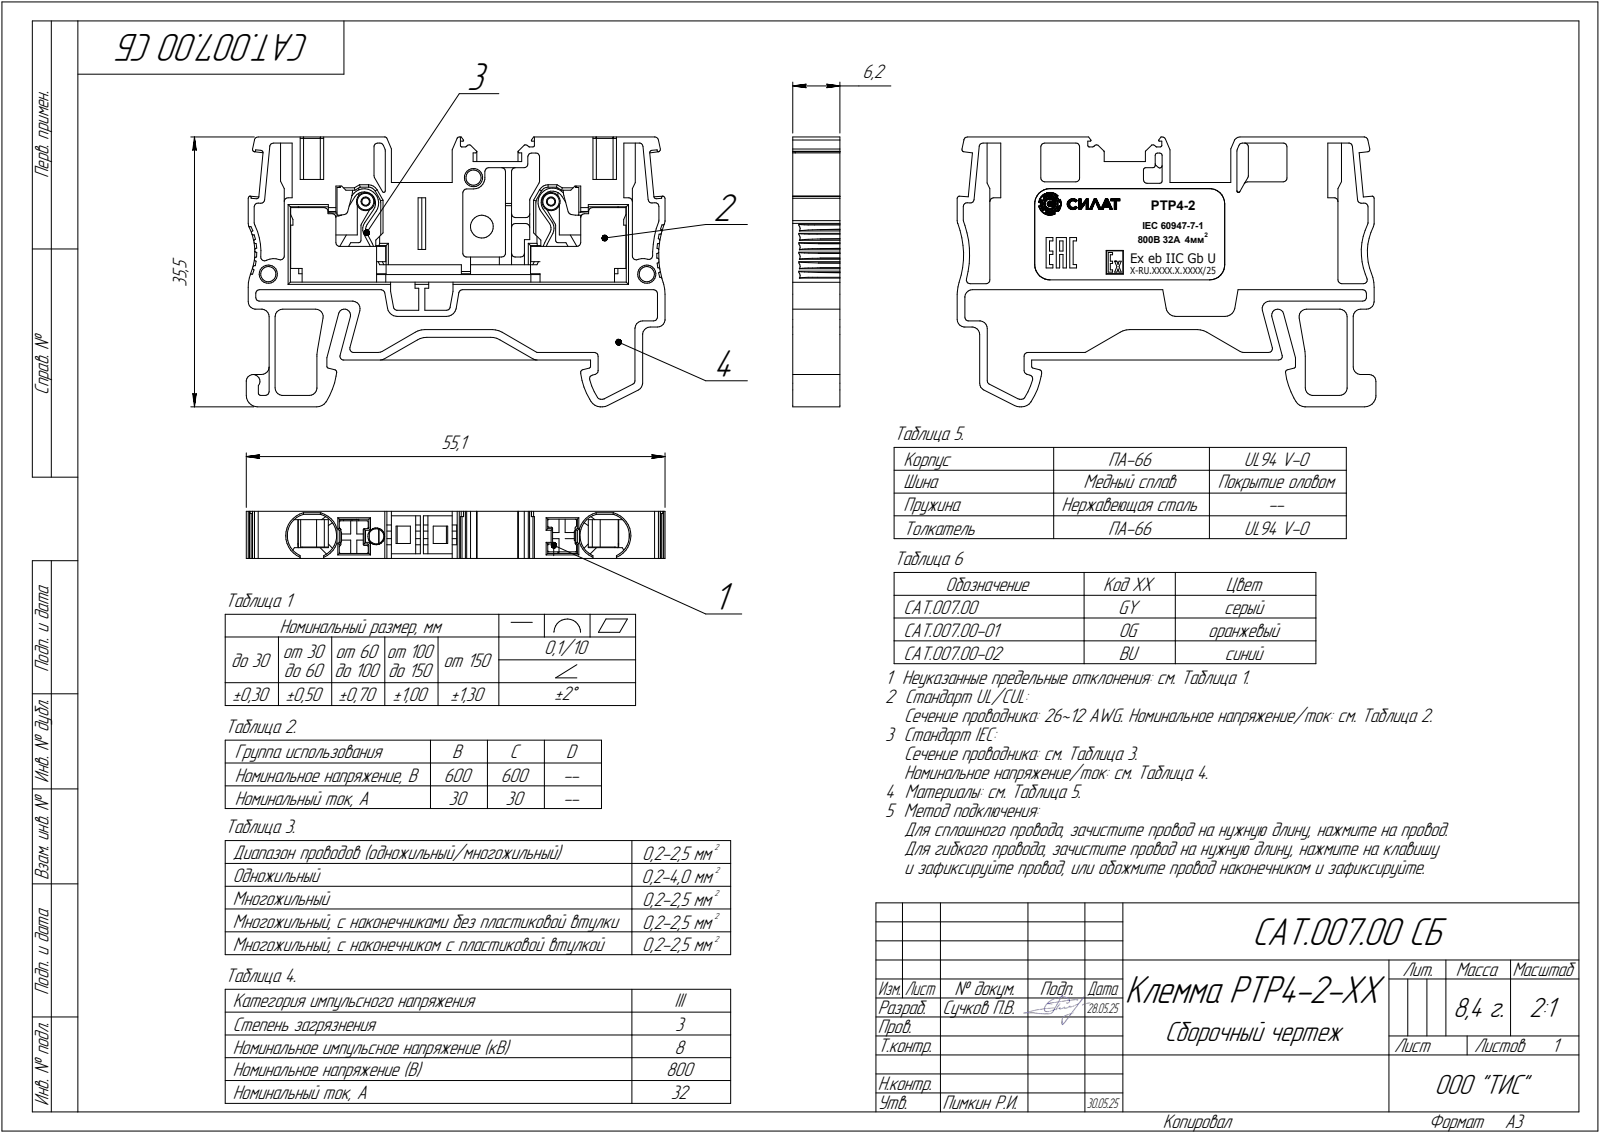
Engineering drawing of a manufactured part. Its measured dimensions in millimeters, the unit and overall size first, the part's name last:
Units: millimetres
Overall size (bounding box): 55.1 × 35.5 × 6.2
Round holes (diameter × count): ⌀2 ×1
Partial cylindrical surfaces — rounded edges, fillets, slot ends (radius × count): R0.15 ×30, R0.3 ×28, R0.5 ×26, R1 ×14, R0.2 ×7, R1.5 ×4, R2.9 ×4, R5 ×3
Main face-to-face distances: 6.2, 0.6, 0.5, 29.35, 3.7, 5.6, 0.4, 4.8, 5.2, 8.5
Volume: 8 357 mm³ · Surface area: 5 202 mm²
Bodies: 1 solid, 442 faces (286 planar, 151 cylindrical, 5 other)
Part name (STEP PRODUCT): Клемма PTP4-2-XX
STEP written by: SolidWorks 2024 (AUTOMOTIVE_DESIGN)
